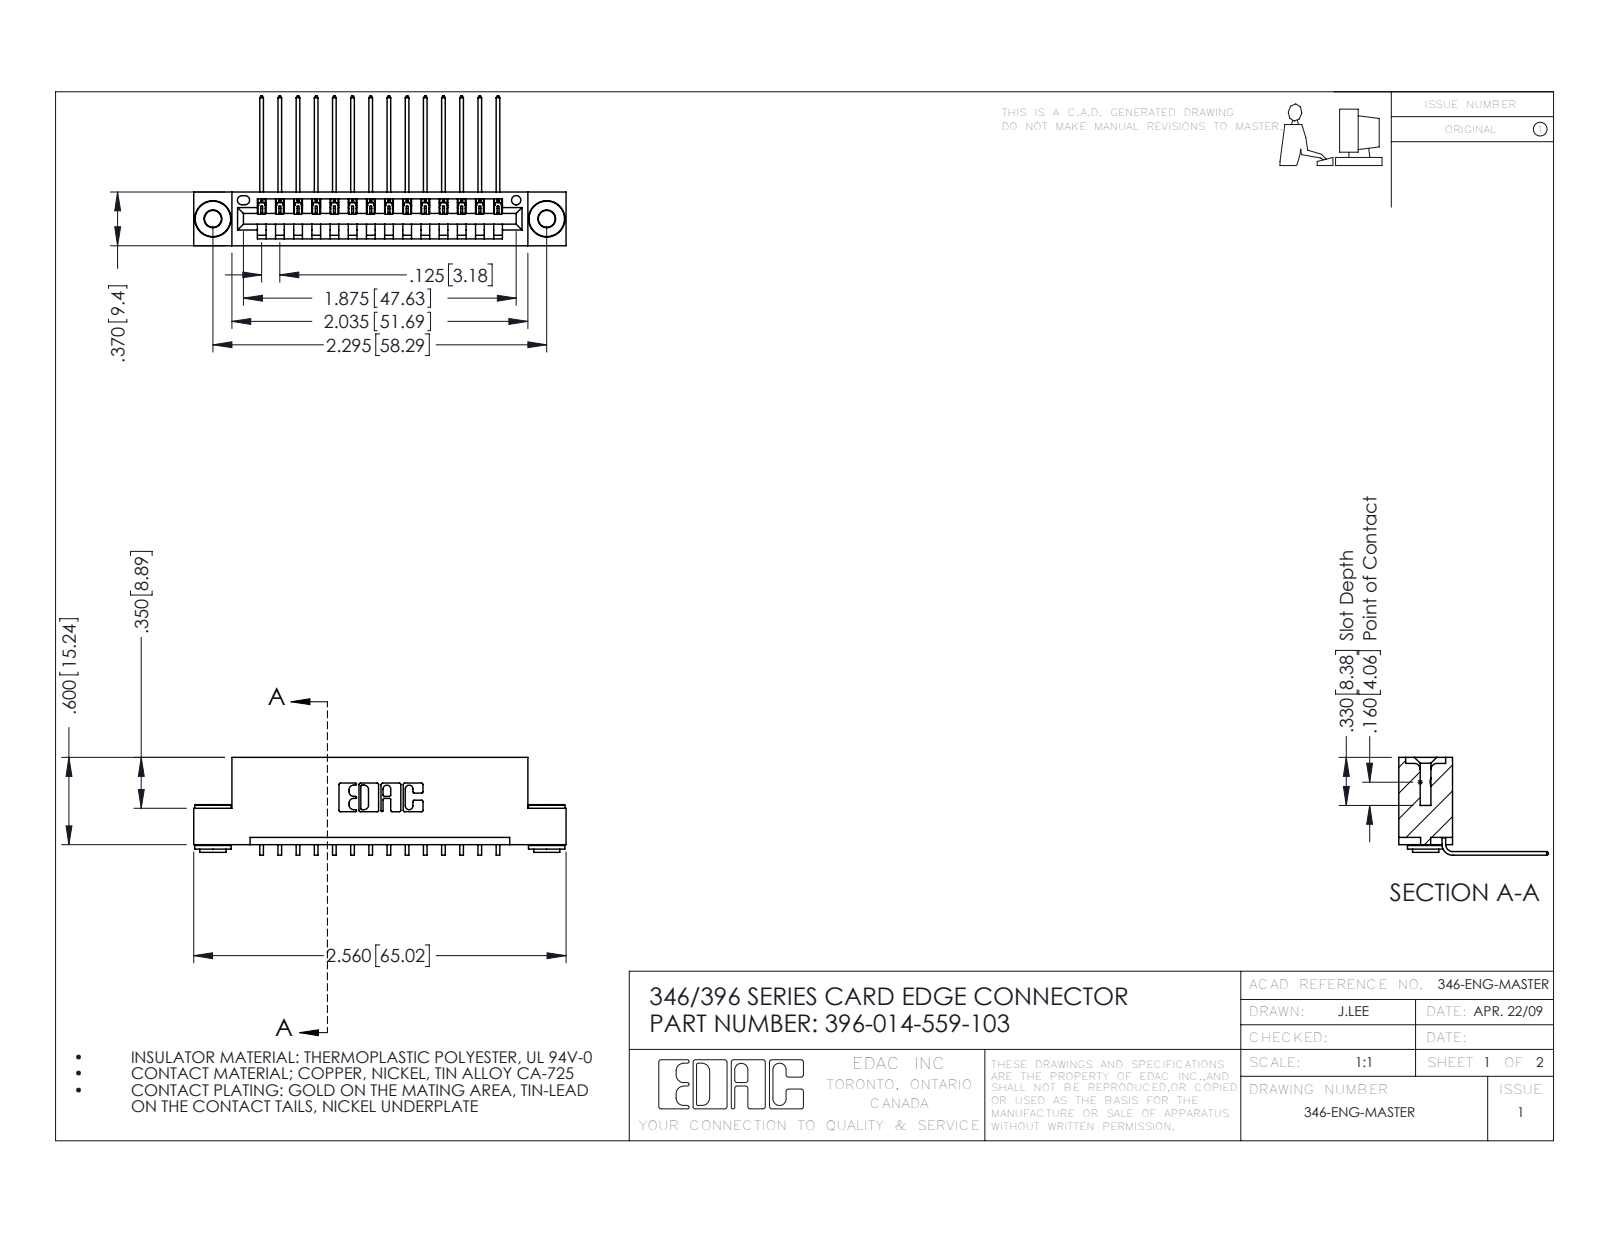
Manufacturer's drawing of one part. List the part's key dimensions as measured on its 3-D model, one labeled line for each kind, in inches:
Part name (STEP PRODUCT): 345-250-002_345-250-002-102; 345-292-001_558 559 Tail - 1; 396-014-559-103; 346 Part_Flush Mounting Lugs - 0.156 Dia-TH
STEP written by: SolidWorks 2016 (CONFIG_CONTROL_DESIGN)
Units: inches
Bodies: 17 solids, 1000 faces (674 planar, 318 cylindrical, 8 other)
Overall size (bounding box): 2.56 × 1.03 × 0.673
Volume: 0.372 in³ · Surface area: 12.12 in²
Round holes (diameter × count): ⌀0.116 ×2, ⌀0.156 ×2, ⌀0.064 ×1
Round bosses / shafts (diameter × count): ⌀0.25 ×2, ⌀0.18 ×2, ⌀0.136 ×2
Partial cylindrical surfaces — rounded edges, fillets, slot ends (radius × count): R0.006 ×28, R0.01 ×22, R0.007 ×6, R0.031 ×6, R0.026 ×3, R0.031 ×2, R0.04 ×2, R0.014 ×1
Main face-to-face distances: 0.048, 0.322, 0.25, 0.37, 0.025, 0.072, 0.298, 0.148, 0.222, 0.1
Hole centre spacings: 0.246, 2.089, 2.295
